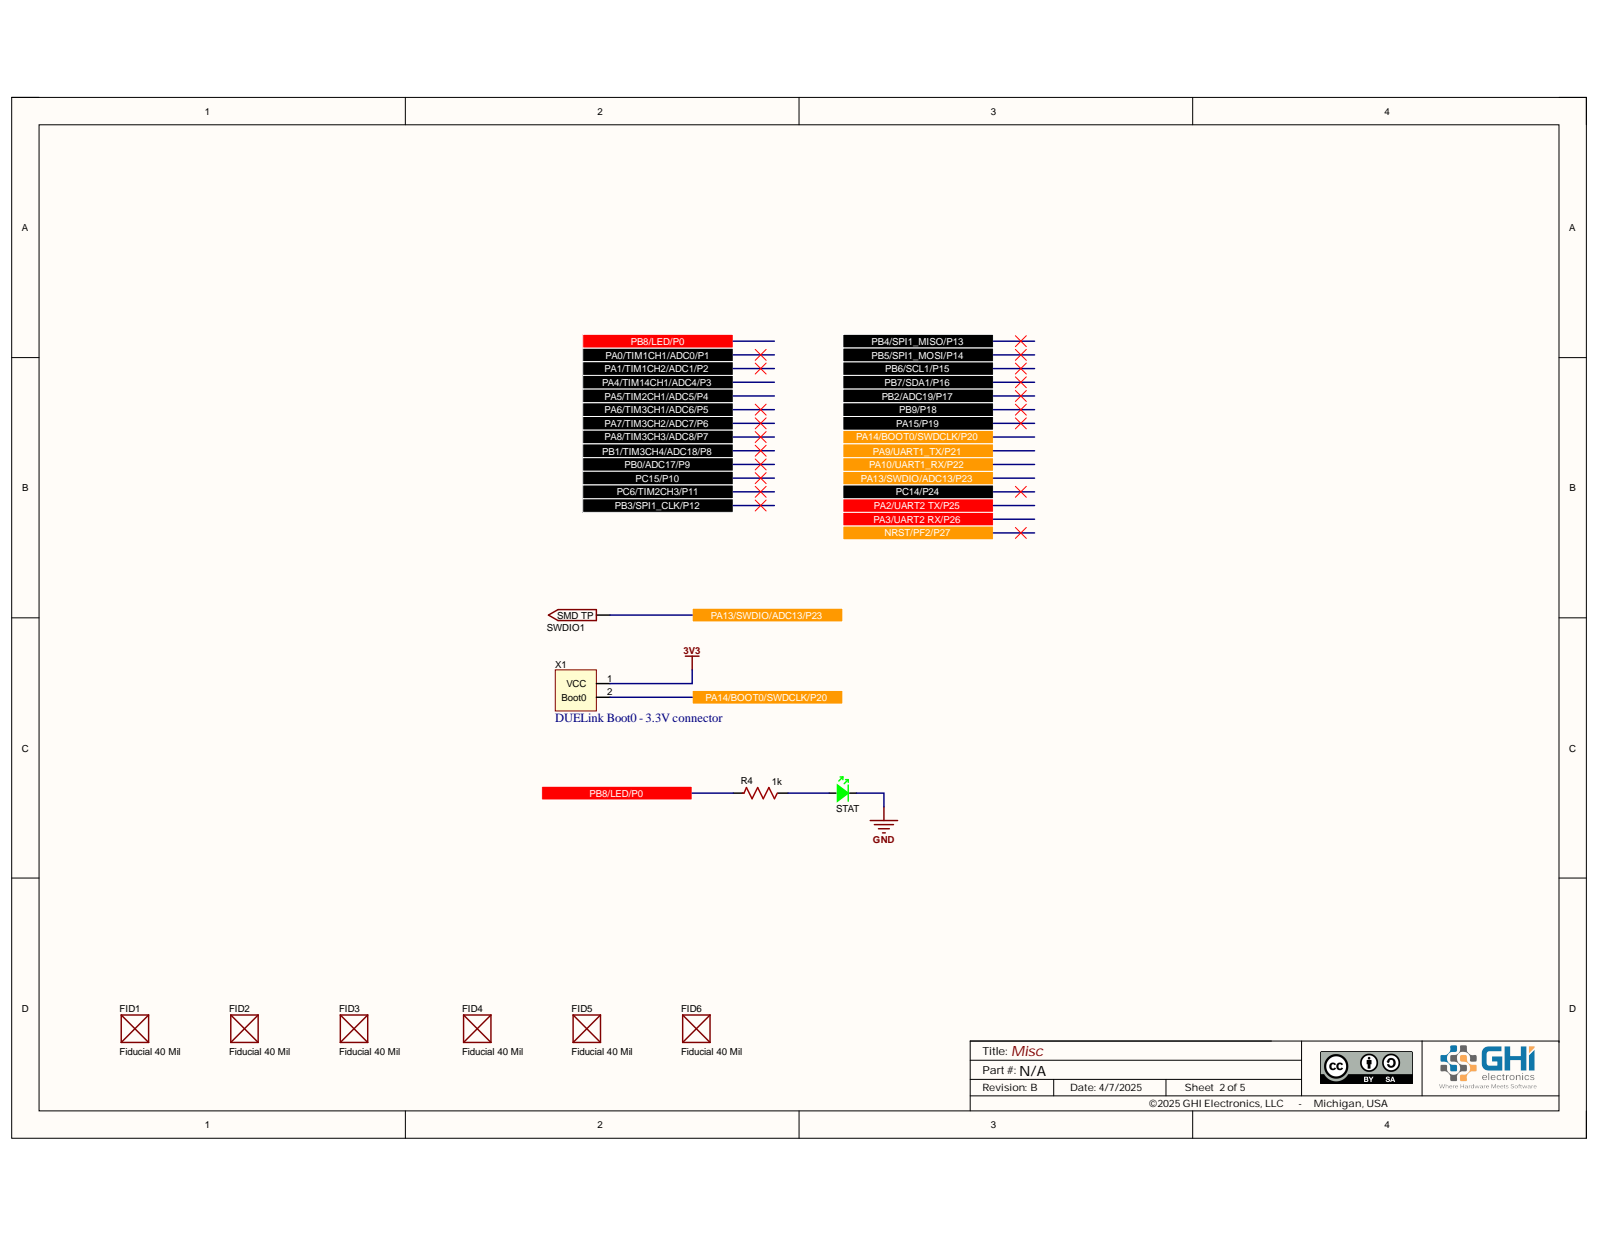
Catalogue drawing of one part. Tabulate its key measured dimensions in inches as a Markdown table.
| quantity | value |
| --- | --- |
| part name | PCB; Board; R4; User Library-R SMD 0402 (+7 more) |
| STEP written by | Open CASCADE 7.5 (AUTOMOTIVE_DESIGN) |
| units | inches |
| bodies | 85 solids, 1407 faces (1091 planar, 216 cylindrical, 100 other) |
| overall size | 1.654 × 1.654 × 0.345 |
| volume | 0.142 in³ |
| surface area | 8.164 in² |
| round holes (diameter × count) | 0.043 × 4, 0.118 × 4, 0.04 × 2 |
| partial cylindrical surfaces (radius × count) | 0.005 × 35, 0.006 × 14, 0.138 × 4, 0.007 × 2, 0.007 × 2, 0.007 × 2, 0.014 × 1, 0.039 × 1 |
| main face-to-face distances | 0.15, 0.236, 0.079, 0.157, 0.228, 0.1, 0.025, 1.083, 0.018, 0.164 |
| hole center spacings | 0.1, 1.378, 0.2, 0.657, 0.749, 0.842, 1.949, 0.216 |
